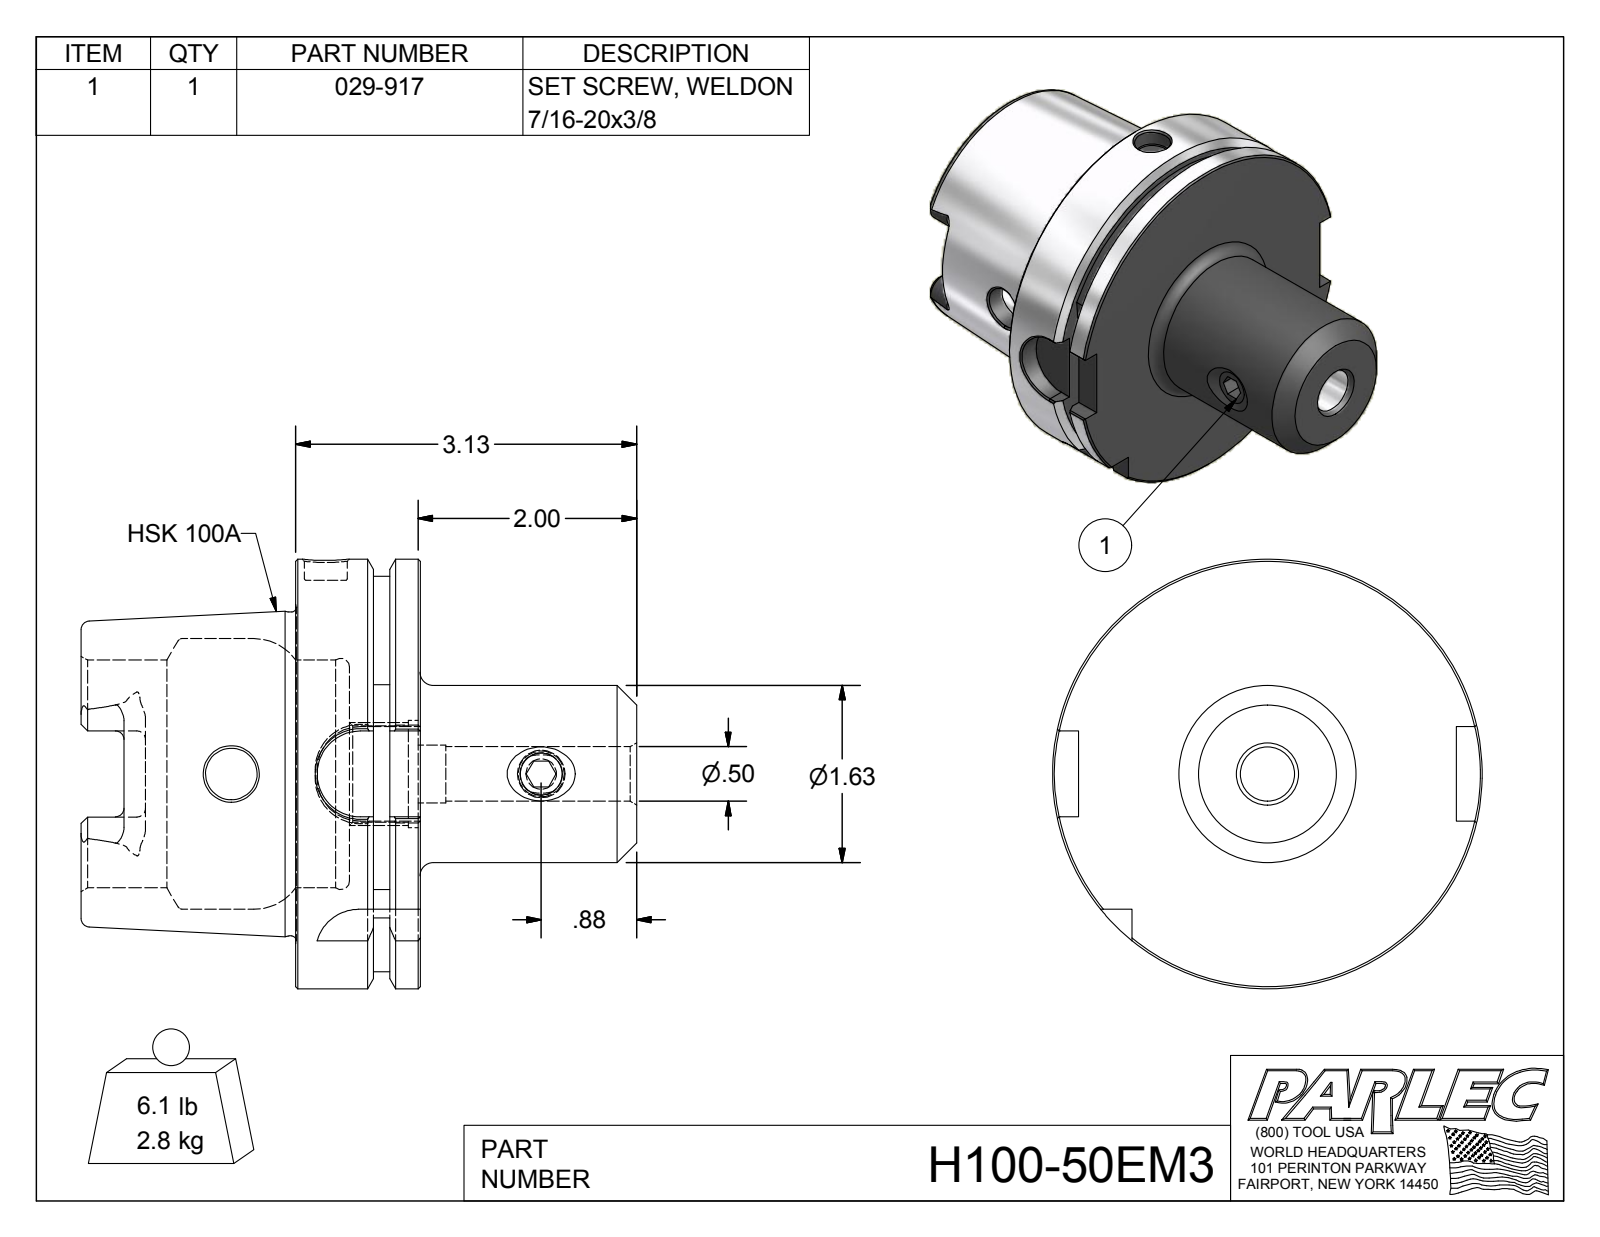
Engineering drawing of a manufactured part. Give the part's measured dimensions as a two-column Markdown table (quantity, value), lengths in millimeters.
| quantity | value |
| --- | --- |
| part name | H100-50EM3; H100-50EM3-1; 029-917 |
| STEP written by | Autodesk Inventor 2012 (AUTOMOTIVE_DESIGN) |
| units | millimeters |
| bodies | 2 solids, 139 faces (52 planar, 35 cylindrical, 52 other) |
| overall size | 129.4 × 100 × 100 |
| volume | 313 200 mm³ |
| surface area | 58 750 mm² |
| round holes (diameter × count) | 9.7 × 1, 10 × 1, 12 × 1, 12.7 × 1, 13.5 × 1, 22.4 × 1, 25 × 1, 53 × 1, 63 × 1 |
| round bosses / shafts (diameter × count) | 100 × 1, 75.4 × 1, 41.3 × 1, 11.1 × 1 |
| partial cylindrical surfaces (radius × count) | 2 × 6, 4.9 × 4, 10 × 4, 46 × 1 |
| main face-to-face distances | 29, 12.5, 16.5, 50, 62.5, 79, 129.4, 79.4, 66.9, 50.4 |
| hole center spacings | 72.2 |
